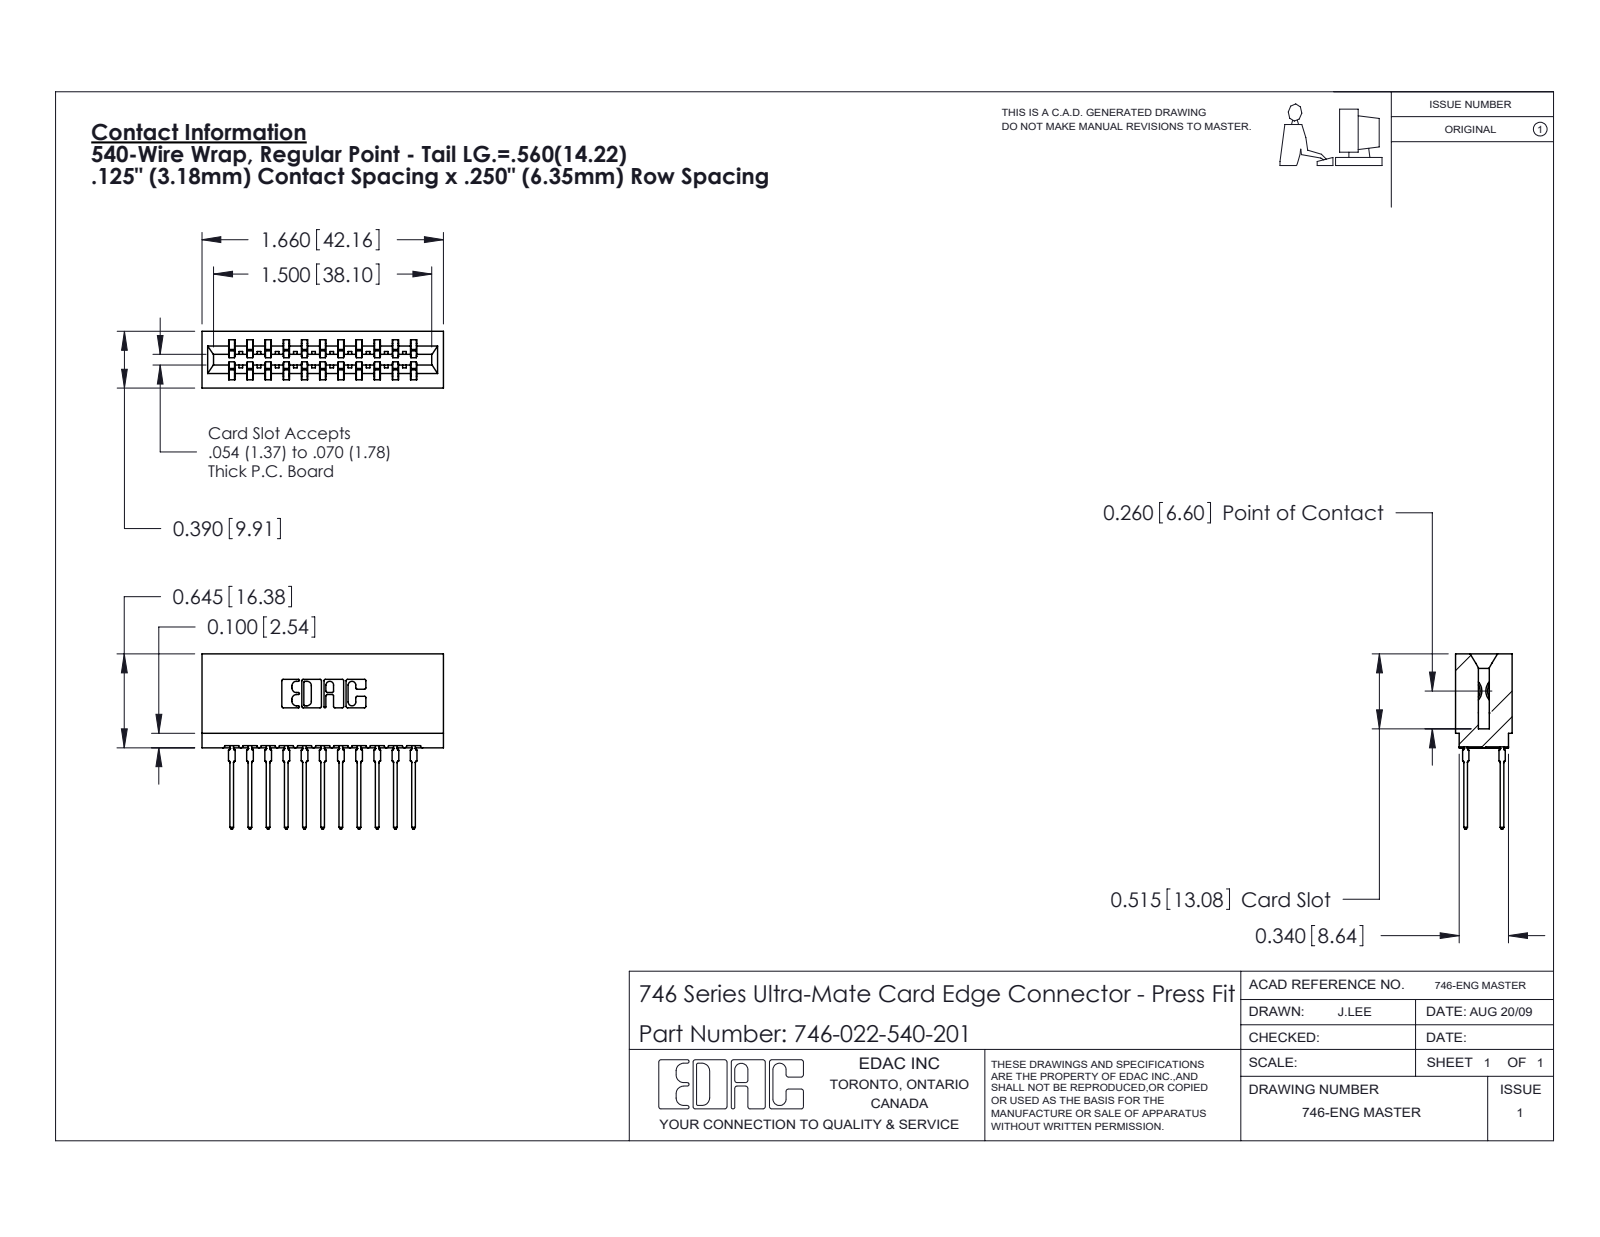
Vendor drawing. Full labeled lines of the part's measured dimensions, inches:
Part name (STEP PRODUCT): 746-292-001_540; 746 Part_.515 Slot Depth - 01; 746-022-540-201
STEP written by: SolidWorks 2020 (CONFIG_CONTROL_DESIGN)
Units: inches
Bodies: 23 solids, 2066 faces (1067 planar, 427 cylindrical, 572 other)
Overall size (bounding box): 1.66 × 1.204 × 0.39
Volume: 0.292 in³ · Surface area: 11.43 in²
Partial cylindrical surfaces — rounded edges, fillets, slot ends (radius × count): R0.021 ×44, R0.01 ×22, R0.015 ×12, R0.005 ×8, R0.011 ×8, R0.007 ×6, R0.031 ×6, R0.026 ×3
Main face-to-face distances: 0.25, 0.333, 0.057, 0.5, 0.083, 0.125, 0.125, 0.39, 0.042, 0.208
